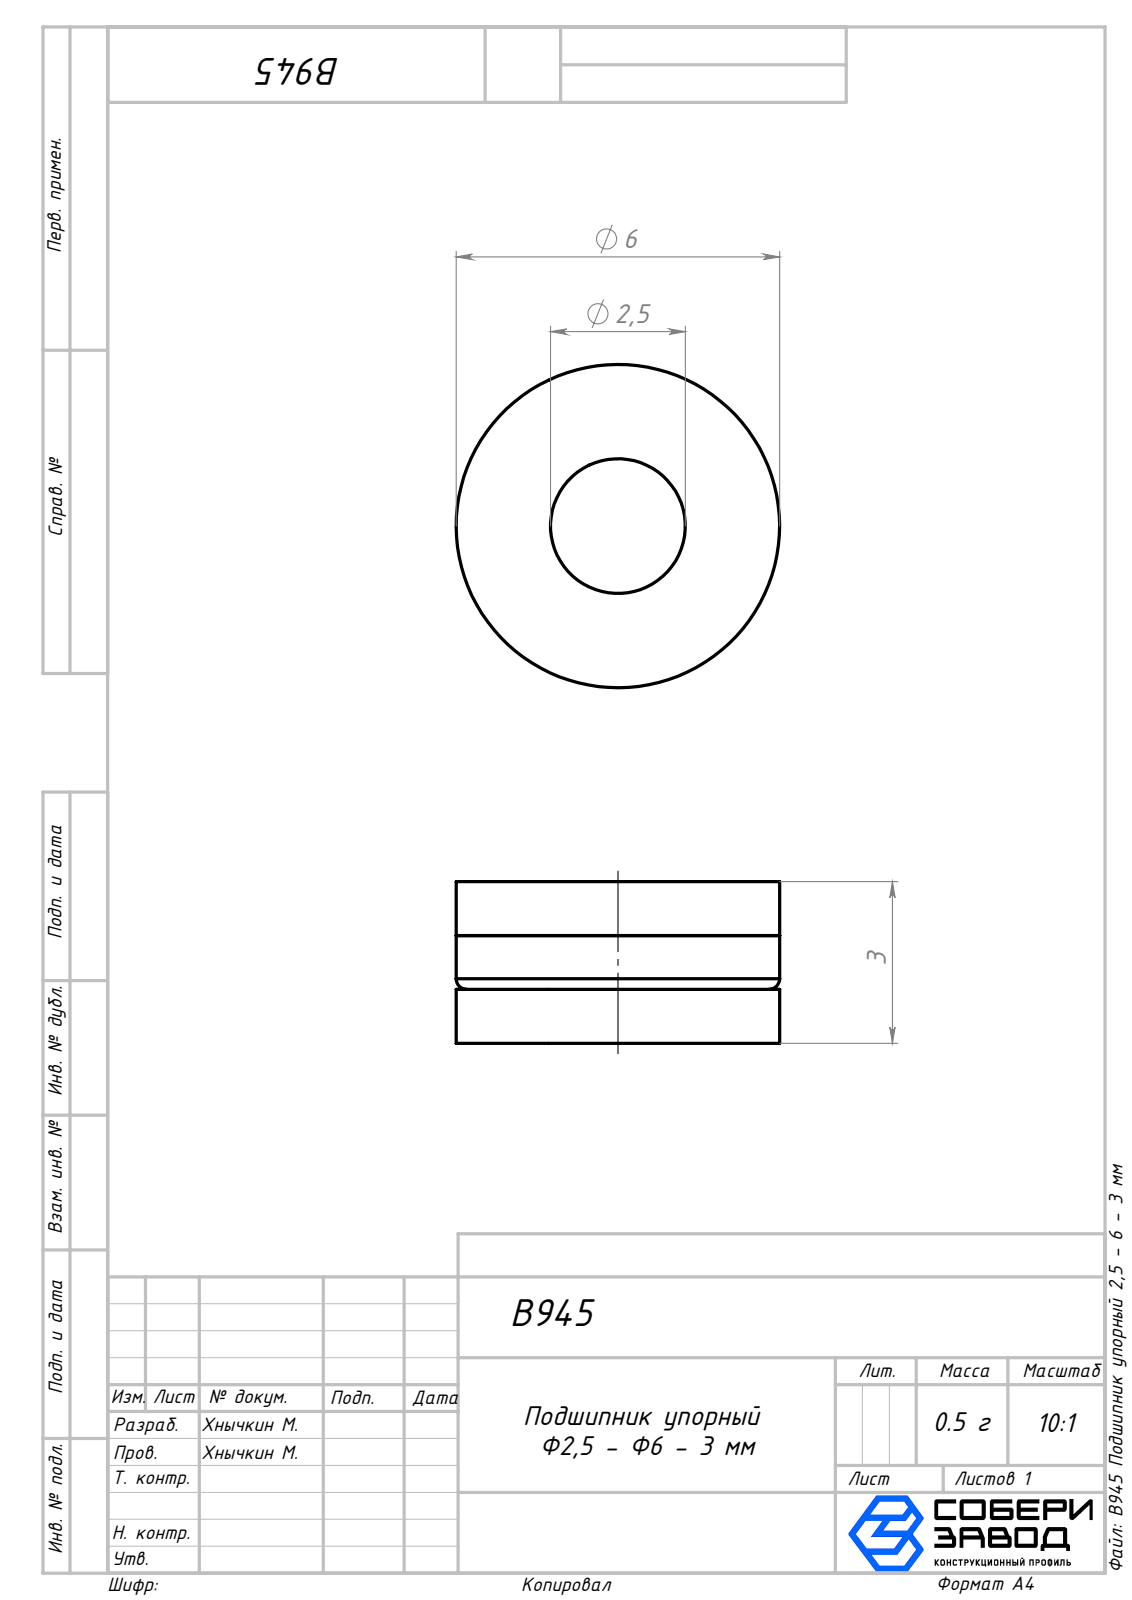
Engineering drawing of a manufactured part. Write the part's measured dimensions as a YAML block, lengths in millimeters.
part_name: "B945 Шарик_00; B945 Первая часть_00; B945 Подшипник упорный 2,5 - 6 - 3 мм; B945 Внутренняя часть_00"
step_written_by: "SolidWorks 2026 (AUTOMOTIVE_DESIGN)"
units: millimeters
bodies: {solids: 12, faces: 74, planar: 12, cylindrical: 34, other: 28}
overall_size: [6, 6, 3]
volume: 57
surface_area: 272
round_holes:
  - {diameter: 1.2, count: 9}
  - {diameter: 2.5, count: 1}
  - {diameter: 5.6, count: 1}
round_bosses_or_shafts:
  - {diameter: 6, count: 1}
  - {diameter: 2.9, count: 1}
face_to_face_distances: [1, 2, 3, 1.1, 0.9, 1.9, 0.8, 2.2, 1.2, 1.4]
hole_center_spacings: [1.45, 2.73, 2.12, 3.68, 4.18, 2.13, 4.19, 2.74]
